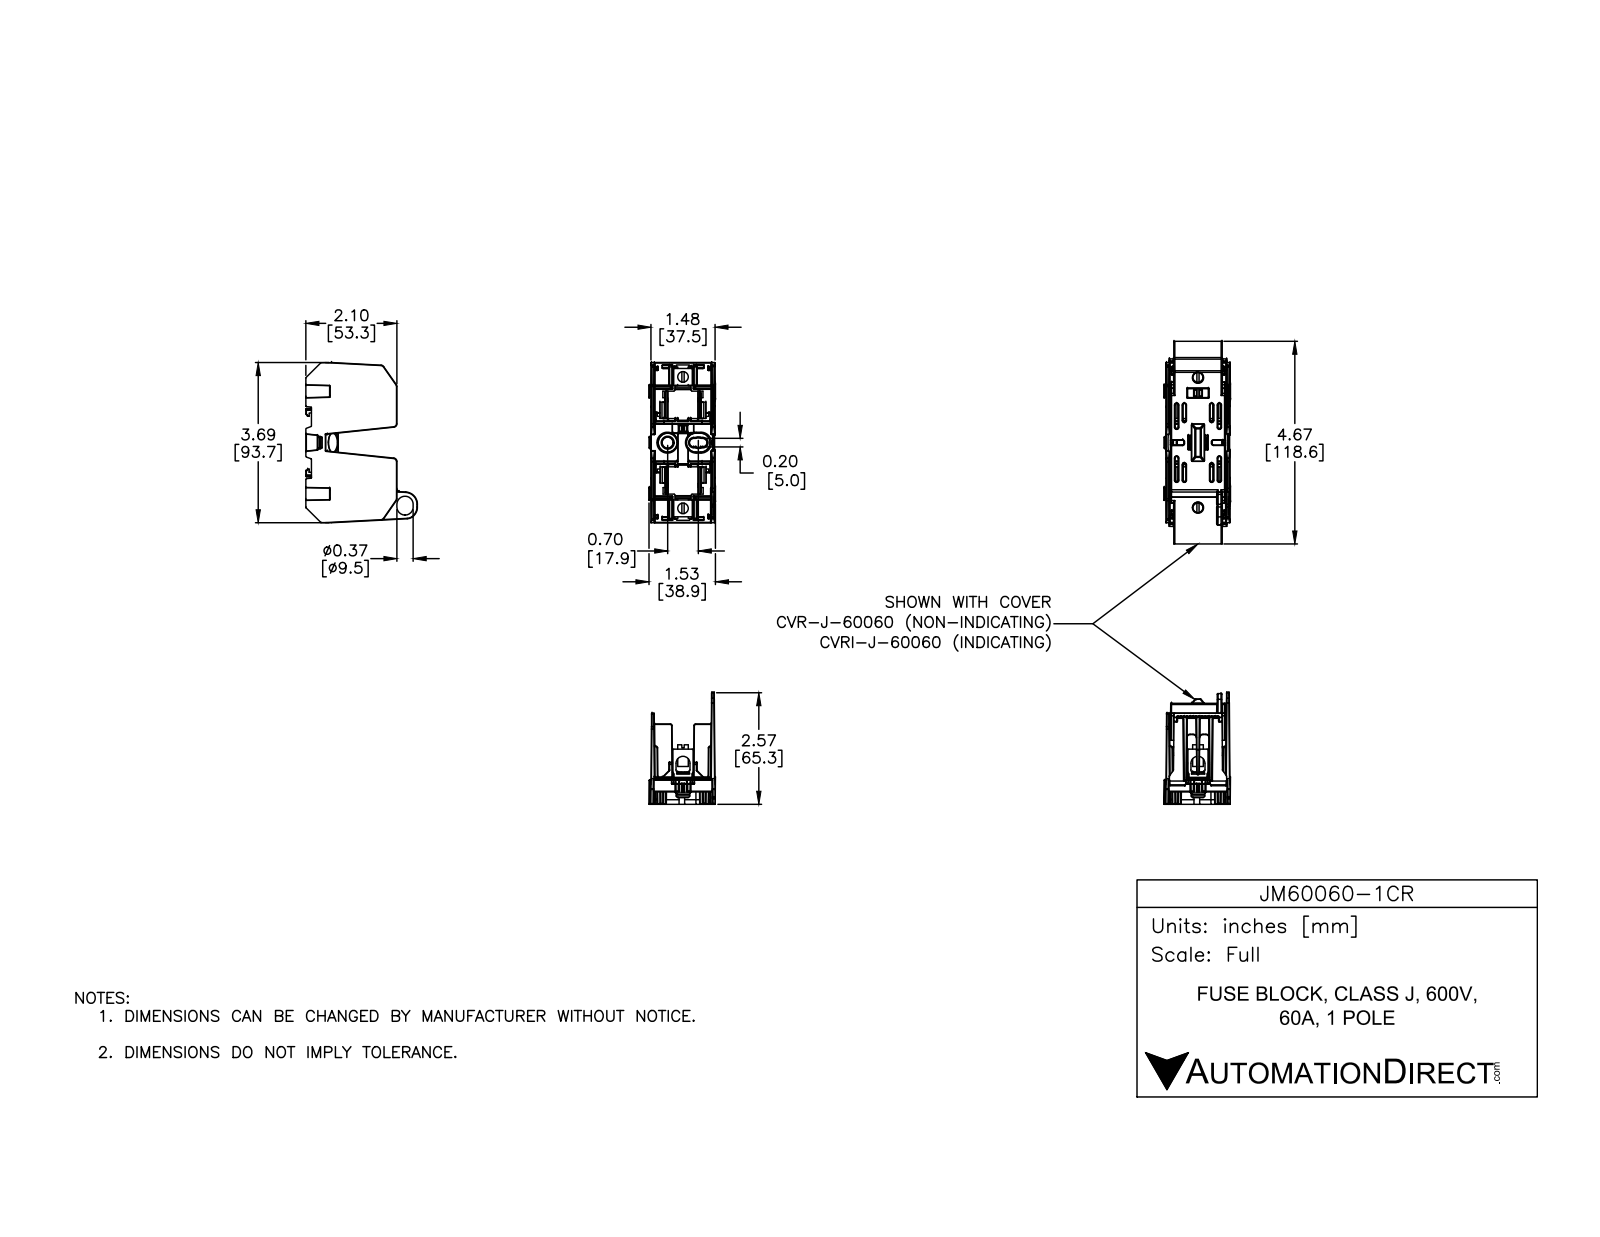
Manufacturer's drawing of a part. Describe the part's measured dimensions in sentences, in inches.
The part is named "JM60060-1CR". Its 3-D file was written by "SolidWorks 2016 (AUTOMOTIVE_DESIGN)". It is 8 solids with 384 faces: 210 planar, 174 cylindrical and 0 other. Overall it measures 3.577 by 1.158 by 1.063 inches. Its volume is 0.355 cubic inches and its surface area 18.3 square inches. Round holes: 2 of diameter 0.225, 2 of diameter 0.244. Round bosses or shafts: 8 of diameter 0.05, 2 of diameter 0.244. Partial cylindrical surfaces (rounded edges, fillets, slot ends): 20 of radius 0.012, 16 of radius 0.039, 8 of radius 0.02, 8 of radius 0.079, 4 of radius 0.01, 4 of radius 0.031, 4 of radius 0.037, 4 of radius 0.05. The main face-to-face distances are 0.032, 0.028, 0.028, 0.06, 0.036, 0.073, 0.041, 0.013, 0.465, 0.39. The hole center spacings are 0.676, 2.352, 1.676, 3.028.
